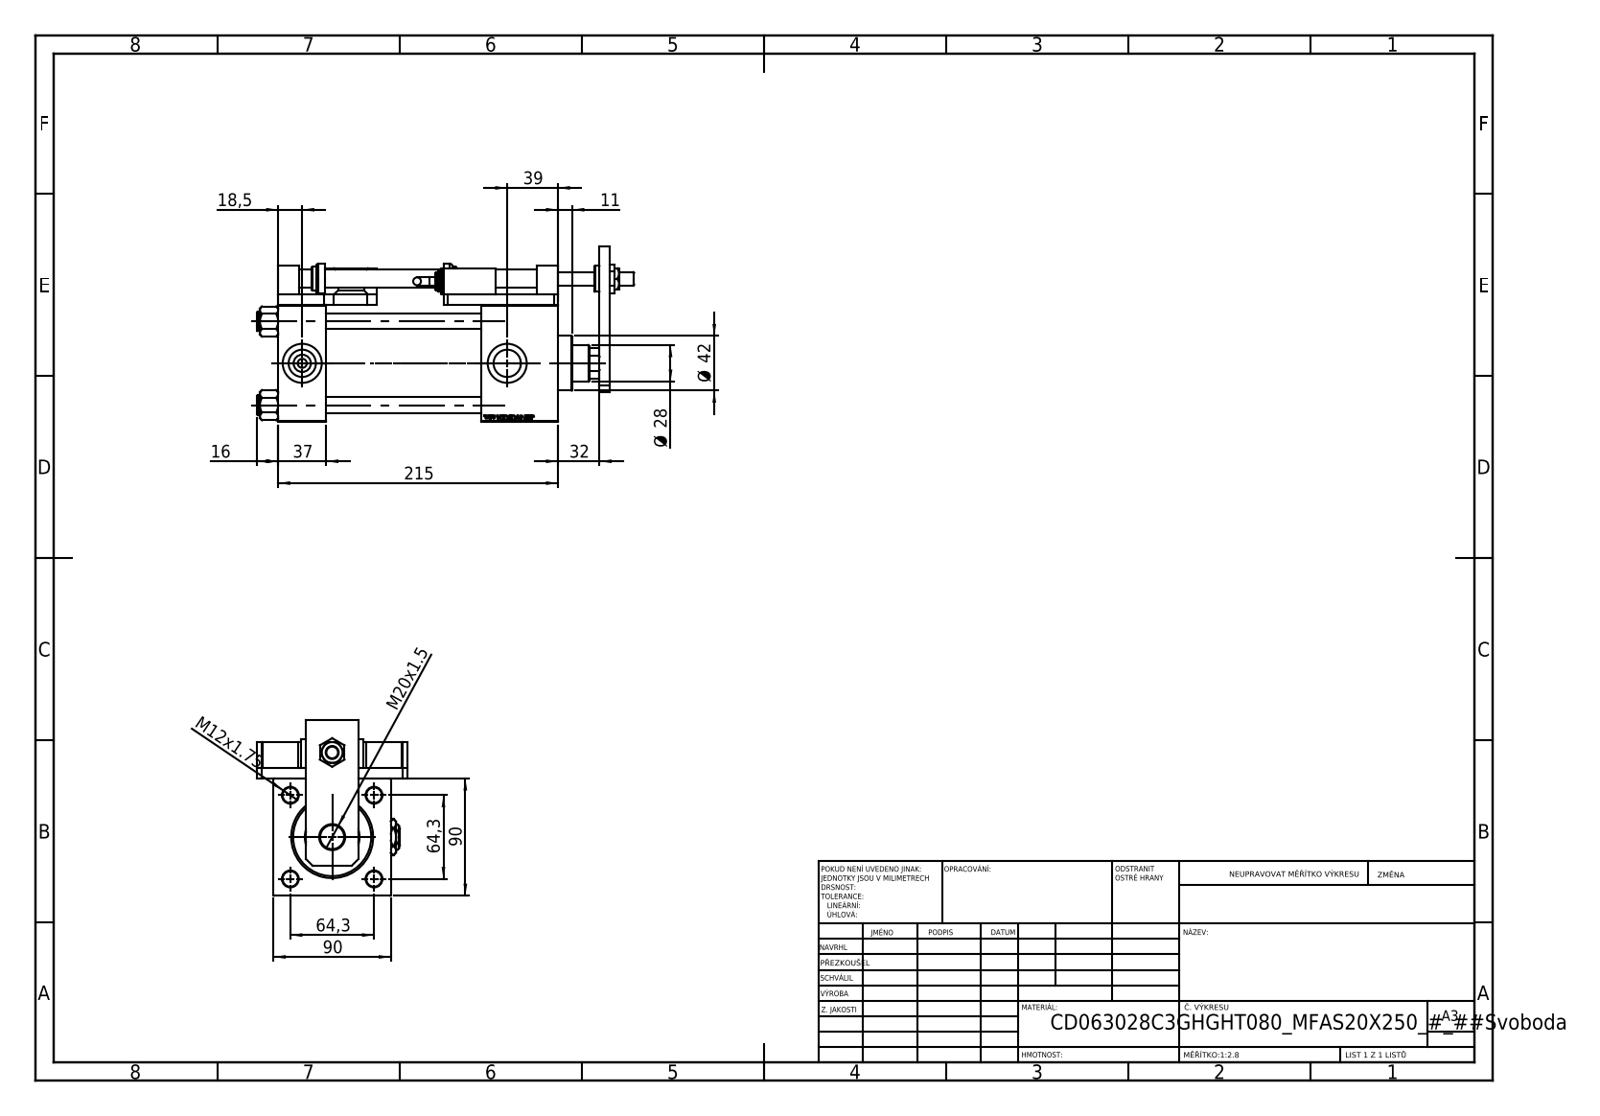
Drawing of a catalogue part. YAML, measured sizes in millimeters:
part_name: "V215CD_C_TYCINKA; V215CD_SWITCH_Q_SWITCH; V215CD_SWITCH_Q_NUT; V215CD_SWITCH_Q_ZARAZKA (+7 more)"
step_written_by: "SolidWorks 2019 (CONFIG_CONTROL_DESIGN)"
units: millimeters
bodies: {solids: 26, faces: 1478, planar: 695, cylindrical: 166, other: 617}
overall_size: [289.5, 135, 115]
volume: 1316000
surface_area: 311002
round_holes:
  - {diameter: 8.5, count: 4}
  - {diameter: 12, count: 4}
  - {diameter: 13.5, count: 4}
  - {diameter: 7, count: 2}
  - {diameter: 20.96, count: 2}
  - {diameter: 30, count: 2}
  - {diameter: 10, count: 1}
  - {diameter: 14, count: 1}
  - {diameter: 18.5, count: 1}
  - {diameter: 20, count: 1}
  - {diameter: 28, count: 1}
  - {diameter: 31, count: 1}
round_bosses_or_shafts:
  - {diameter: 15, count: 4}
  - {diameter: 20, count: 3}
  - {diameter: 16, count: 2}
  - {diameter: 14, count: 2}
  - {diameter: 6, count: 2}
  - {diameter: 69, count: 1}
  - {diameter: 42, count: 1}
  - {diameter: 23, count: 1}
partial_cylinders:
  - {radius: 7.5, count: 4}
  - {radius: 13.5, count: 1}
face_to_face_distances: [8, 90, 37, 98, 215, 178, 40, 32, 91, 59]
hole_center_spacings: [45.47, 64.3, 32, 45.96, 90.93, 102.33, 199, 201.56]
